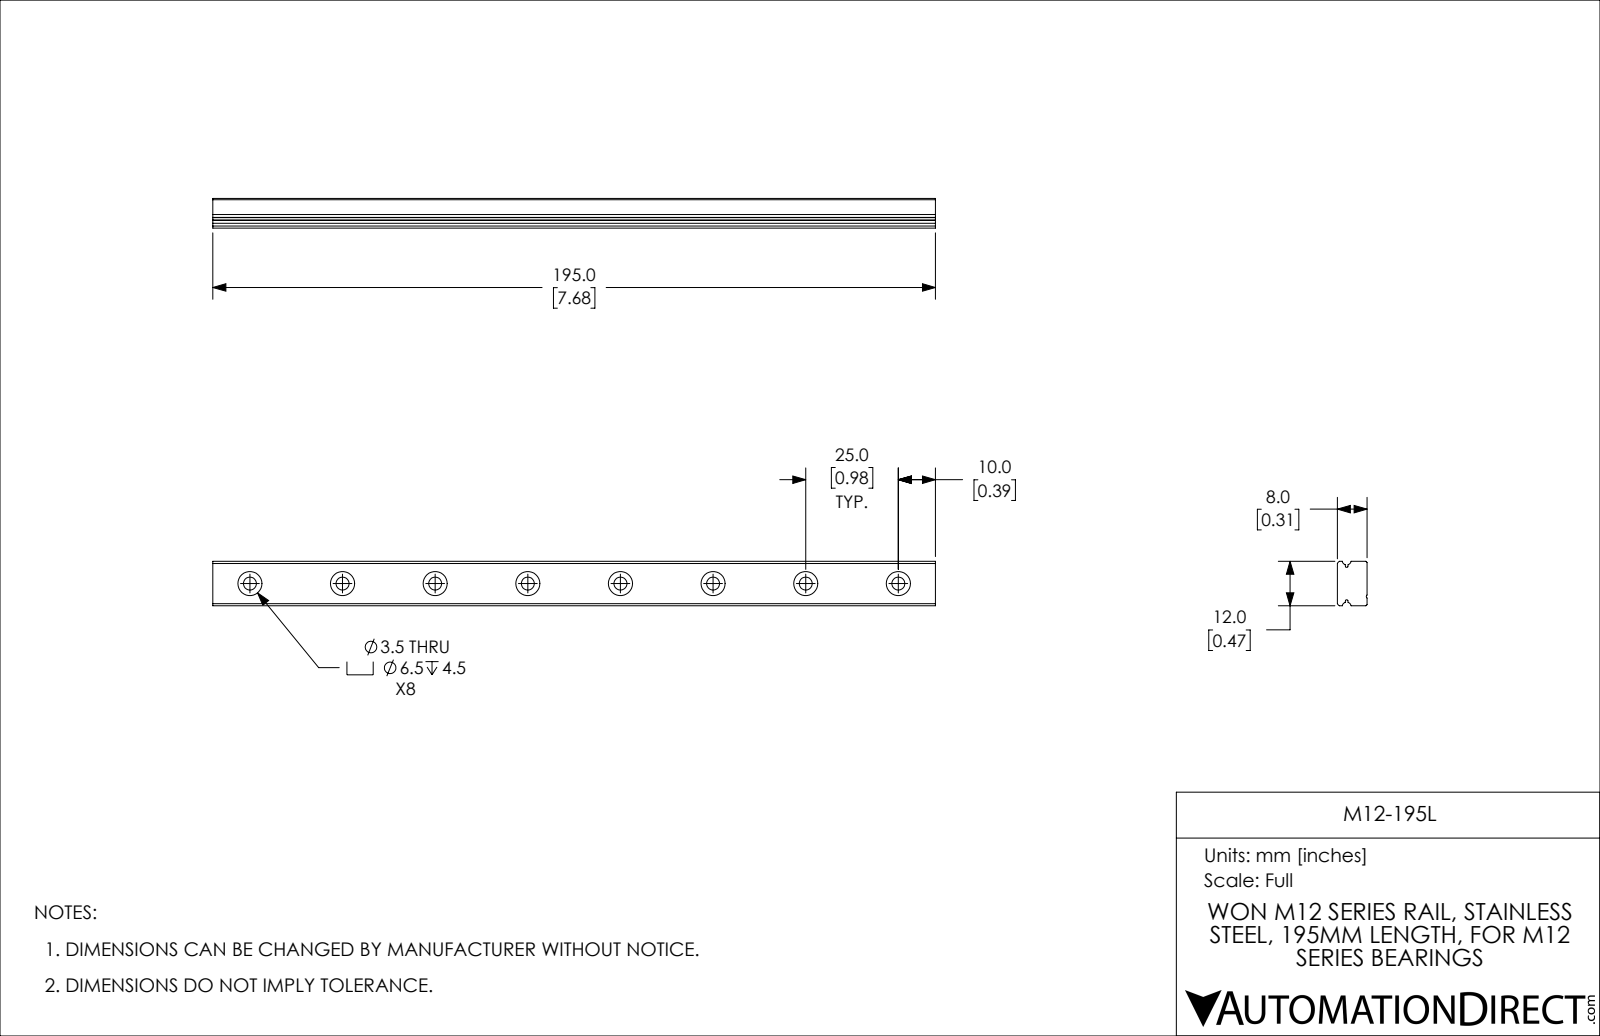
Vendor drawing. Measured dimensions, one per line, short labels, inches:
name: M12-195L
written by: SolidWorks 2019 (CONFIG_CONTROL_DESIGN)
unit: in
bodies: 1 solid, 65 faces (21 planar, 44 cylindrical, 0 other)
size: 7.677 × 0.472 × 0.315
volume: 0.996 in³; area: 14.7 in²
holes: 8× ⌀0.138, 8× ⌀0.256
rounds: 2× R0.017, 2× R0.039, 2× R0.045, 2× R0.047, 1× R0.02
face distances: 0.315, 0.472, 0.023, 0.138, 0.177, 7.677
hole spacings: 0.984, 1.969, 2.953, 3.937, 4.921, 5.906, 6.89
